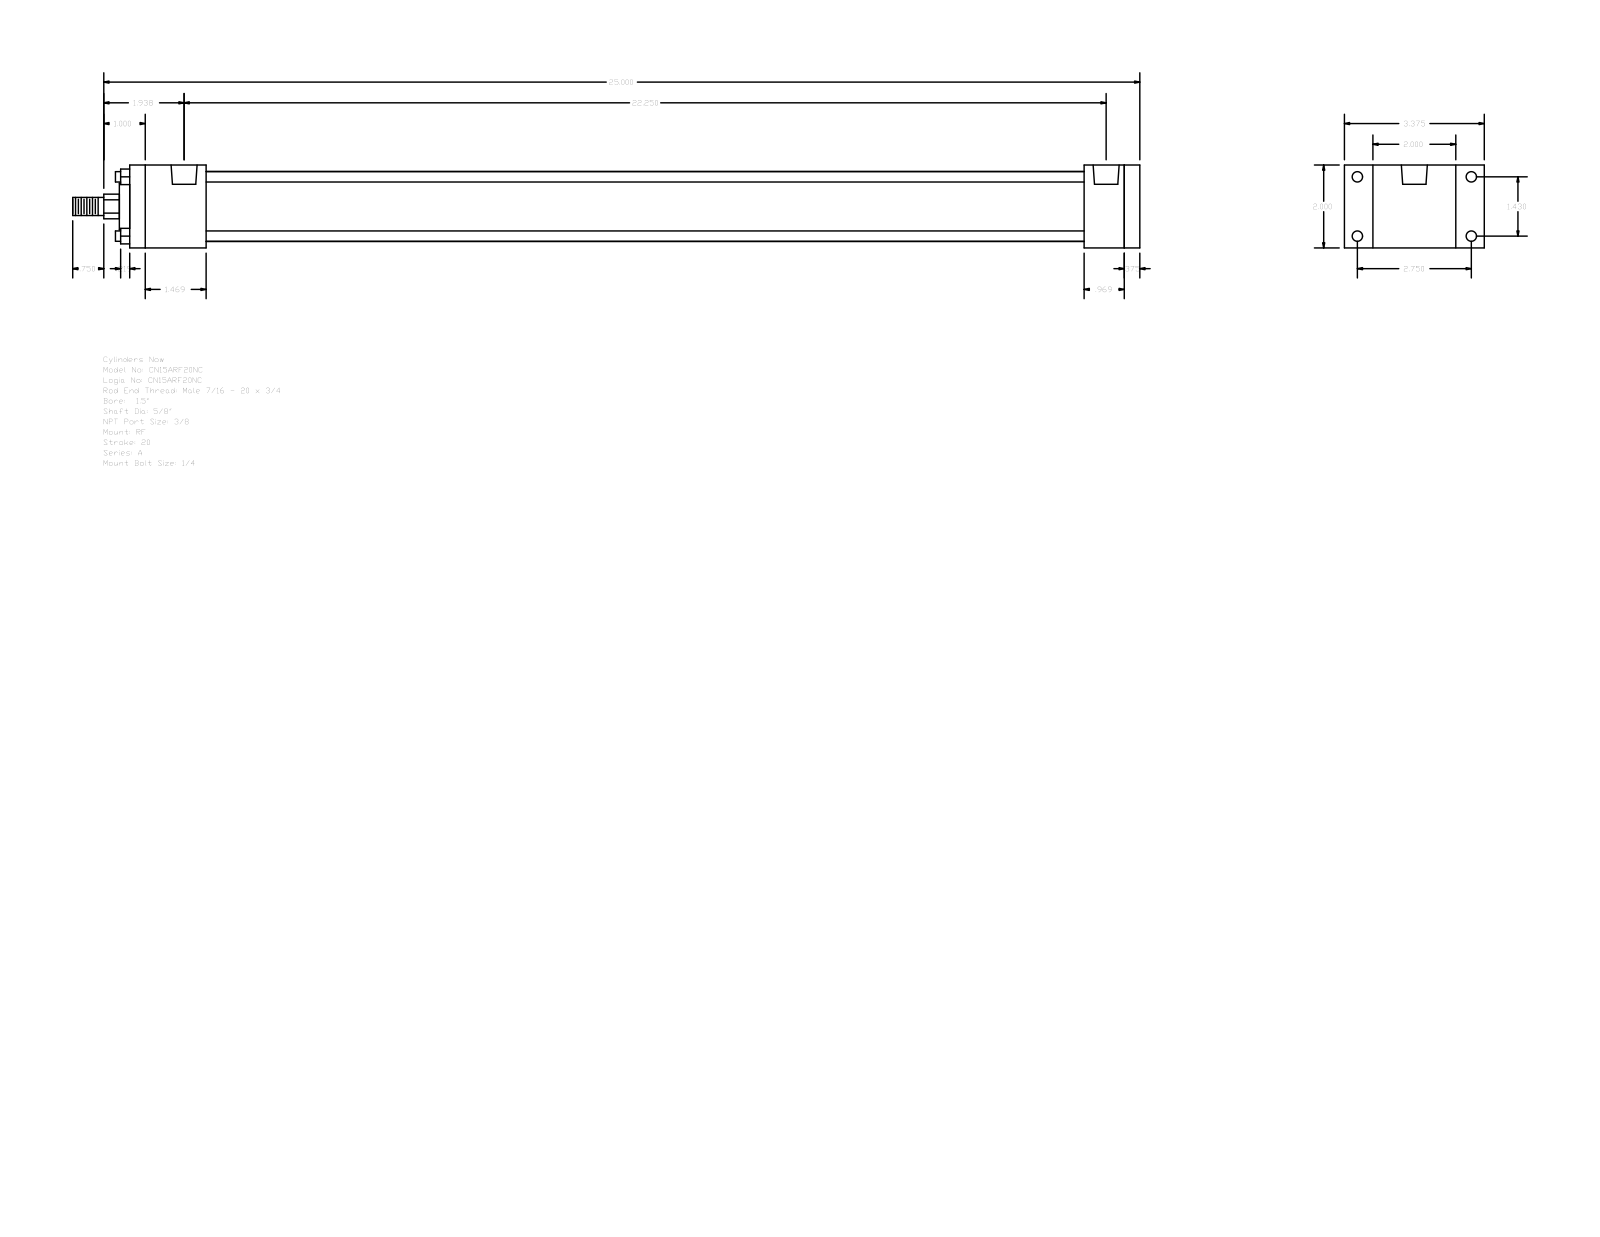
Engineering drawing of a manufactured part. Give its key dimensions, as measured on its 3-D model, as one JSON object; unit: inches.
{"part_name": "A_RF__0150_0.625", "step_written_by": "GSSL Pune (CONFIG_CONTROL_DESIGN)", "units": "inches", "bodies": {"solids": 0, "faces": 92, "planar": 64, "cylindrical": 28, "other": 0}, "overall_size": [25.75, 3.375, 2], "round_holes": [[0.219, 4], [0.25, 4], [0.627, 2]], "round_bosses_or_shafts": [[0.25, 4], [1.69, 1], [1.125, 1], [0.625, 1], [0.437, 1]], "partial_cylinders_radius": [[0.297, 1]], "face_to_face_distances": [2, 0.375, 24, 24.375, 23.031, 0.969, 1.344, 1.844, 21.187, 22.156], "hole_center_spacings": [0.156, 1.43, 2.75, 3.099, 21.937, 22.094, 22.25]}
